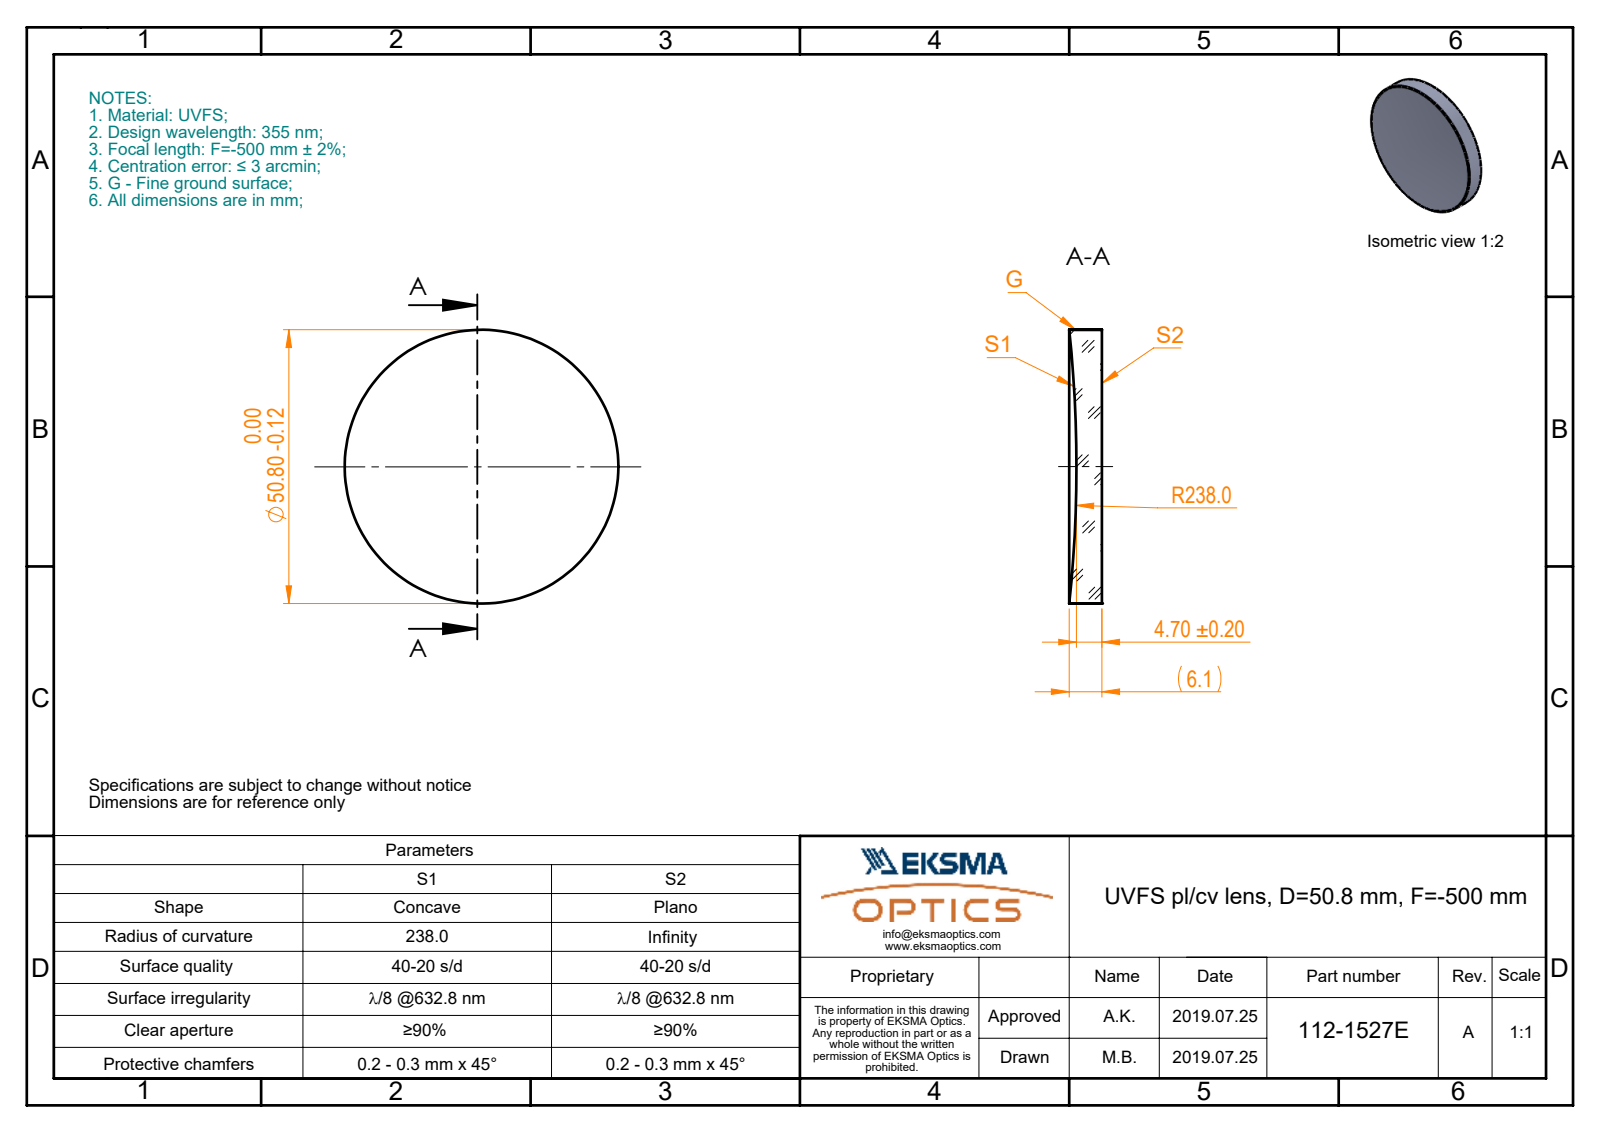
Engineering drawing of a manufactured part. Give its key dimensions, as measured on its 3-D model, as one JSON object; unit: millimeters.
{"part_name": "112-1527E UVFS pl-cv 50.8 F-500", "step_written_by": "SolidWorks 2017 (CONFIG_CONTROL_DESIGN)", "units": "millimeters", "bodies": {"solids": 1, "faces": 5, "planar": 1, "cylindrical": 2, "other": 2}, "overall_size": [50.8, 50.8, 6.06], "volume_mm3": 10902, "surface_area_mm2": 5026, "round_bosses_or_shafts": [[50.8, 1]]}
